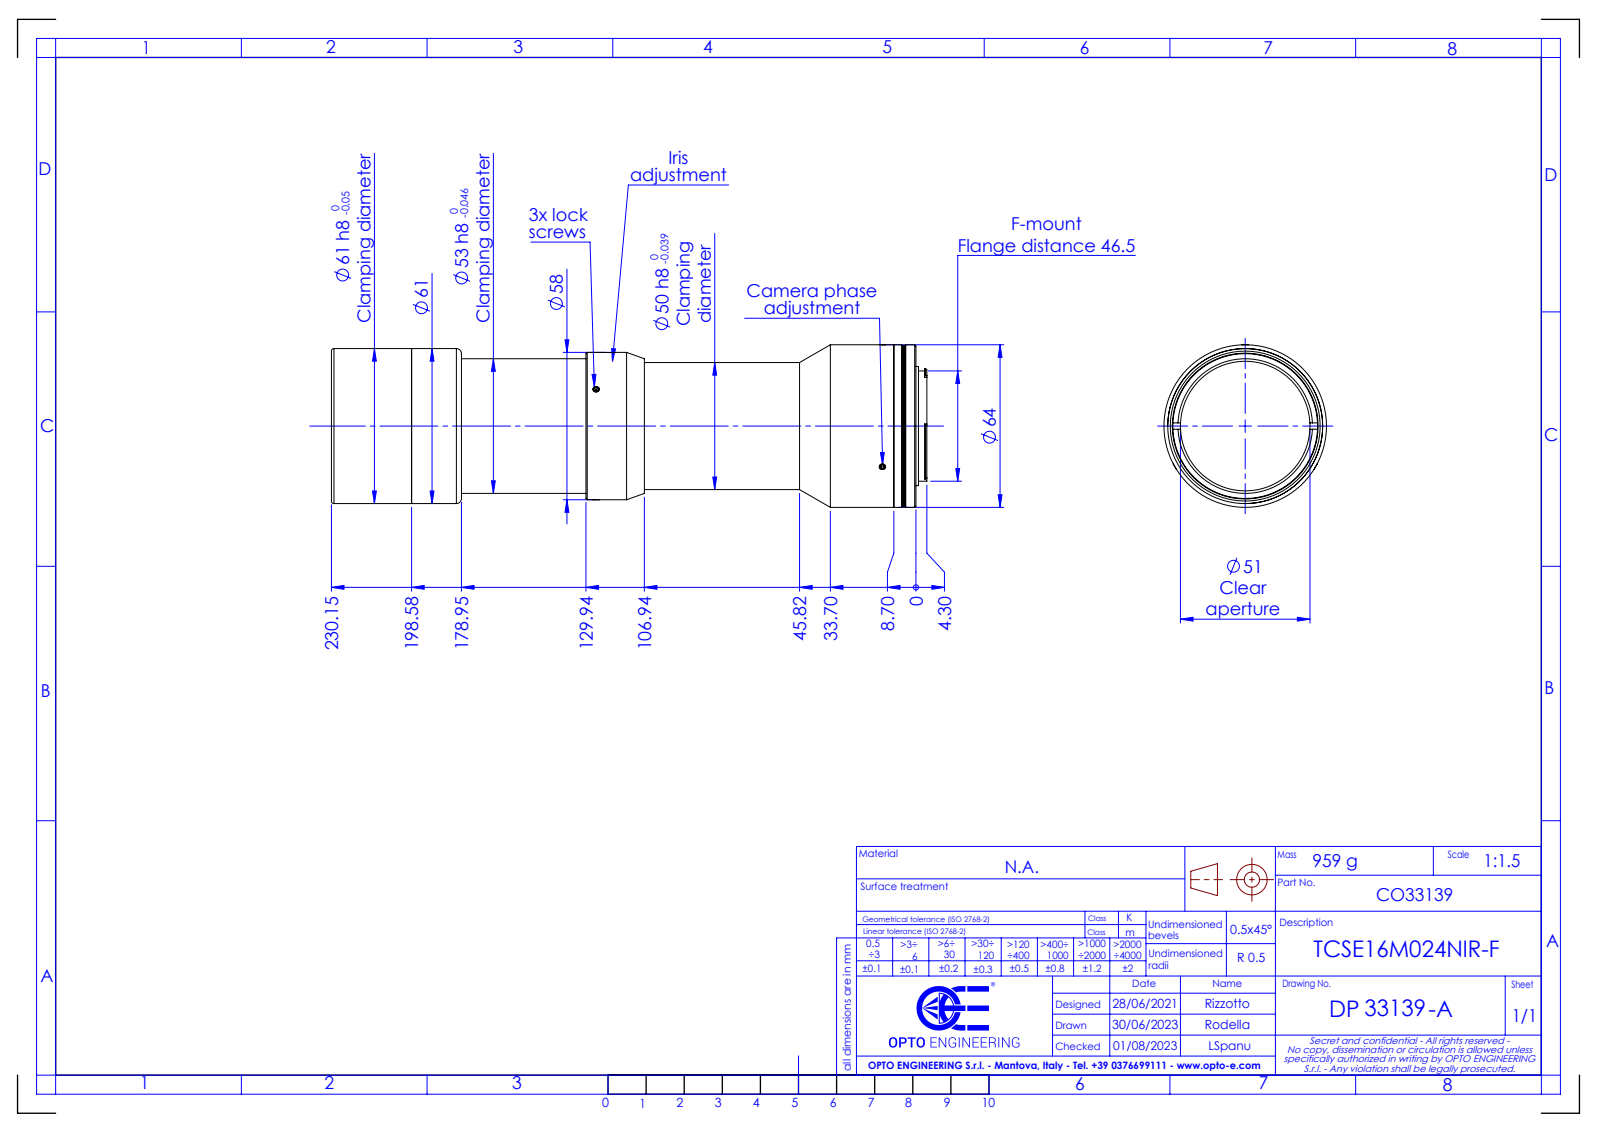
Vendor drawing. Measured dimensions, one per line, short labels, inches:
name: DP33139-A_TCSE16M024NIR-F
written by: SolidWorks 2021 (CONFIG_CONTROL_DESIGN)
unit: in
bodies: 0 solids, 166 faces (73 planar, 55 cylindrical, 38 other)
size: 9.23 × 2.52 × 2.52
holes: 2× ⌀0.098, 1× ⌀0.165, 1× ⌀1.654, 1× ⌀2.008, 1× ⌀2.244
bosses: 1× ⌀2.52, 1× ⌀2.5, 1× ⌀2.402, 1× ⌀2.283, 1× ⌀2.087, 1× ⌀1.969, 1× ⌀1.846, 1× ⌀1.709
rounds: 6× R0.02, 2× R0.045, 1× R0.892
face distances: 0.157, 0.185, 0.224, 5.115, 0.039, 4.891, 4.958, 0.067, 4.93, 0.028
